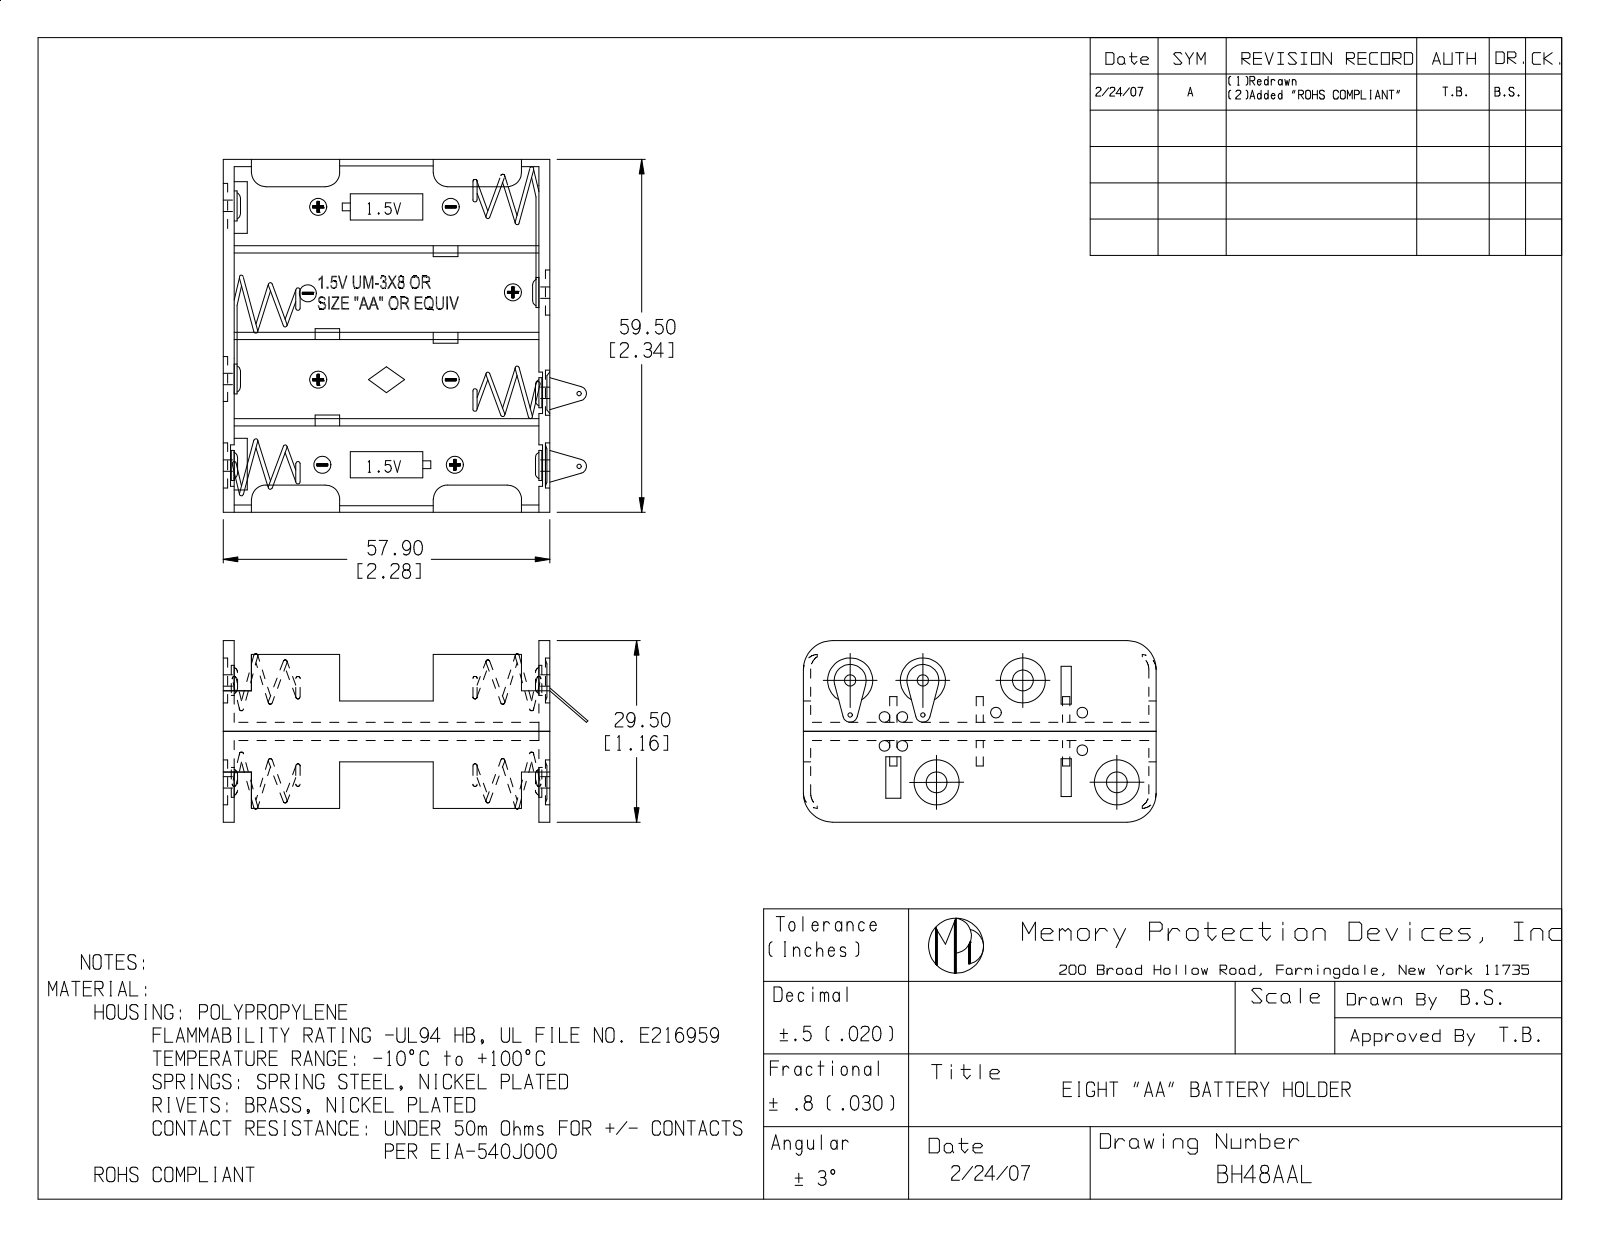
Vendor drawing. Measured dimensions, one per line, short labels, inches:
name: BH48AAL
written by: SolidWorks 2012 (CONFIG_CONTROL_DESIGN)
unit: in
bodies: 1 solid, 10 faces (6 planar, 4 cylindrical, 0 other)
size: 2.34 × 2.28 × 1.16
volume: 6.111 in³; area: 20.54 in²
rounds: 4× R0.2
face distances: 1.16, 2.28, 2.34
